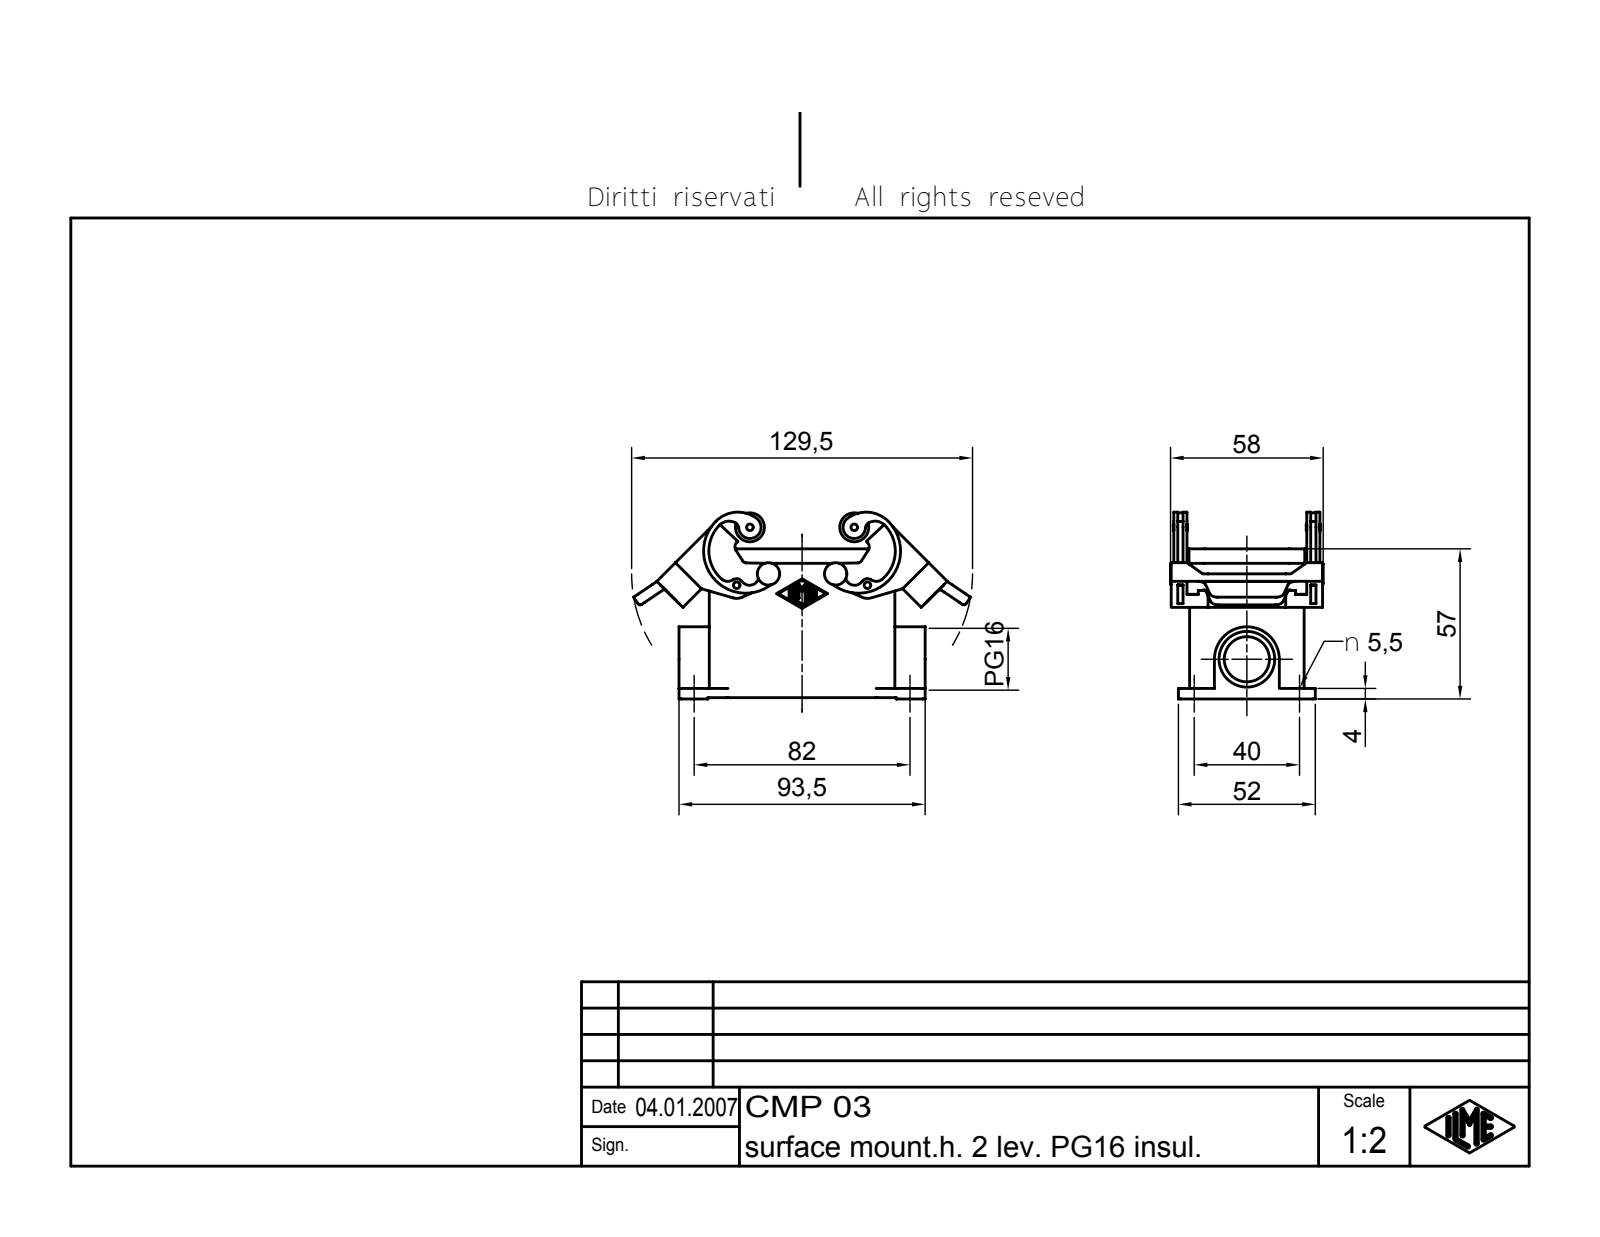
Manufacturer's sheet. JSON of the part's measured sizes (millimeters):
{"part_name": "CMP 03", "step_written_by": "Autodesk Inventor 7 (AUTOMOTIVE_DESIGN)", "units": "millimeters", "bodies": {"solids": 1, "faces": 749, "planar": 191, "cylindrical": 205, "other": 353}, "overall_size": [127.99, 70.94, 58], "volume_mm3": 88465, "surface_area_mm2": 50953, "round_holes": [[2, 4], [5.5, 4], [2.5, 2], [17.16, 1], [21.16, 1]], "round_bosses_or_shafts": [[11, 2], [5, 2], [3, 2]], "partial_cylinders_radius": [[1, 20], [0.38, 14], [3, 12], [6, 8], [2.5, 6], [1.5, 4], [2, 4], [3.5, 4]], "face_to_face_distances": [3, 40.5, 3.5, 43.5, 4, 37.5, 50.5, 56.5, 0.75, 4.5], "hole_center_spacings": [22.56, 40, 49.78, 82, 91.24, 39.64, 49.68]}
